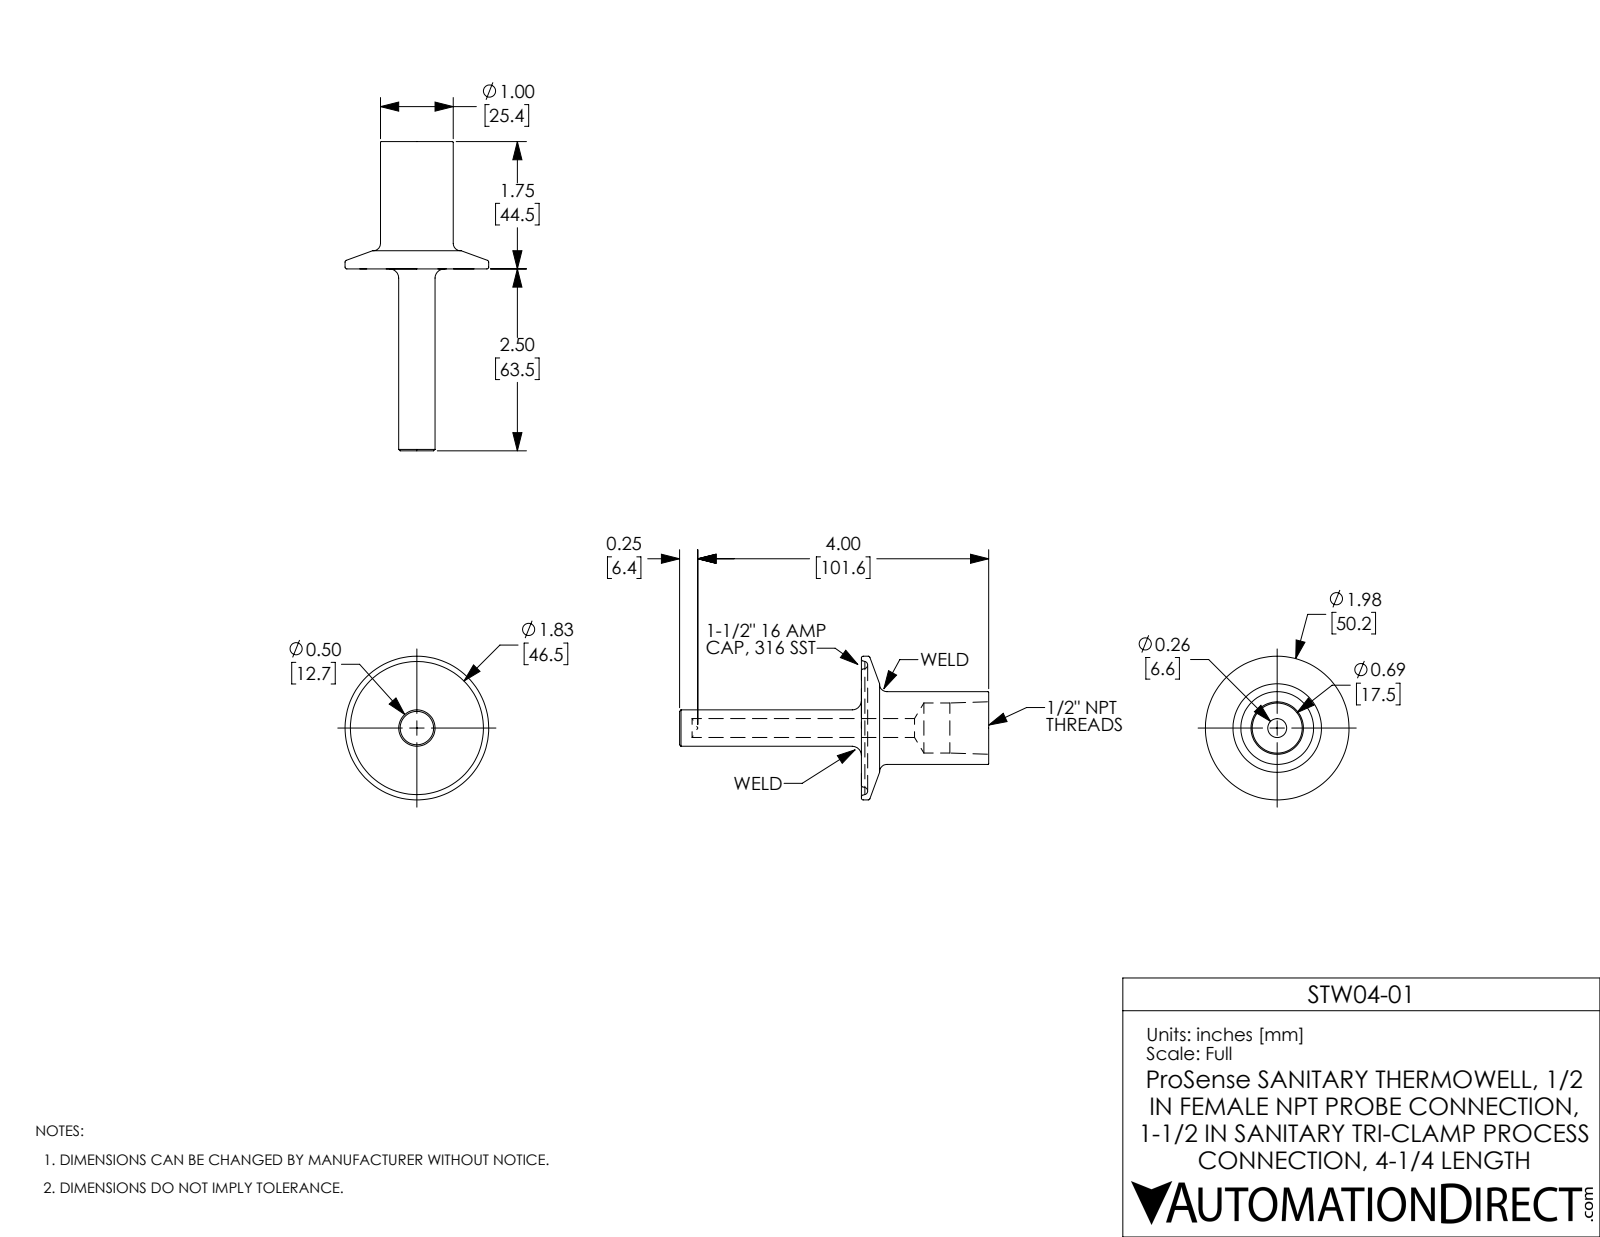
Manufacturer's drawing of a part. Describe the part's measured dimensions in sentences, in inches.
The part is named "STW04-01". Its 3-D file was written by "SolidWorks 2017 (AUTOMOTIVE_DESIGN)". It is 1 solid with 45 faces: 5 planar, 10 cylindrical and 30 other. Overall it measures 4.25 by 1.975 by 1.975 inches. Its volume is 1.734 cubic inches and its surface area 20.25 square inches. Round holes: 1 of diameter 0.26, 1 of diameter 0.688. Round bosses or shafts: 1 of diameter 1.975, 1 of diameter 1, 1 of diameter 0.5. The main face-to-face distances are 1.75, 4.25, 2.5, 1.5, 0.25, 2.75.
